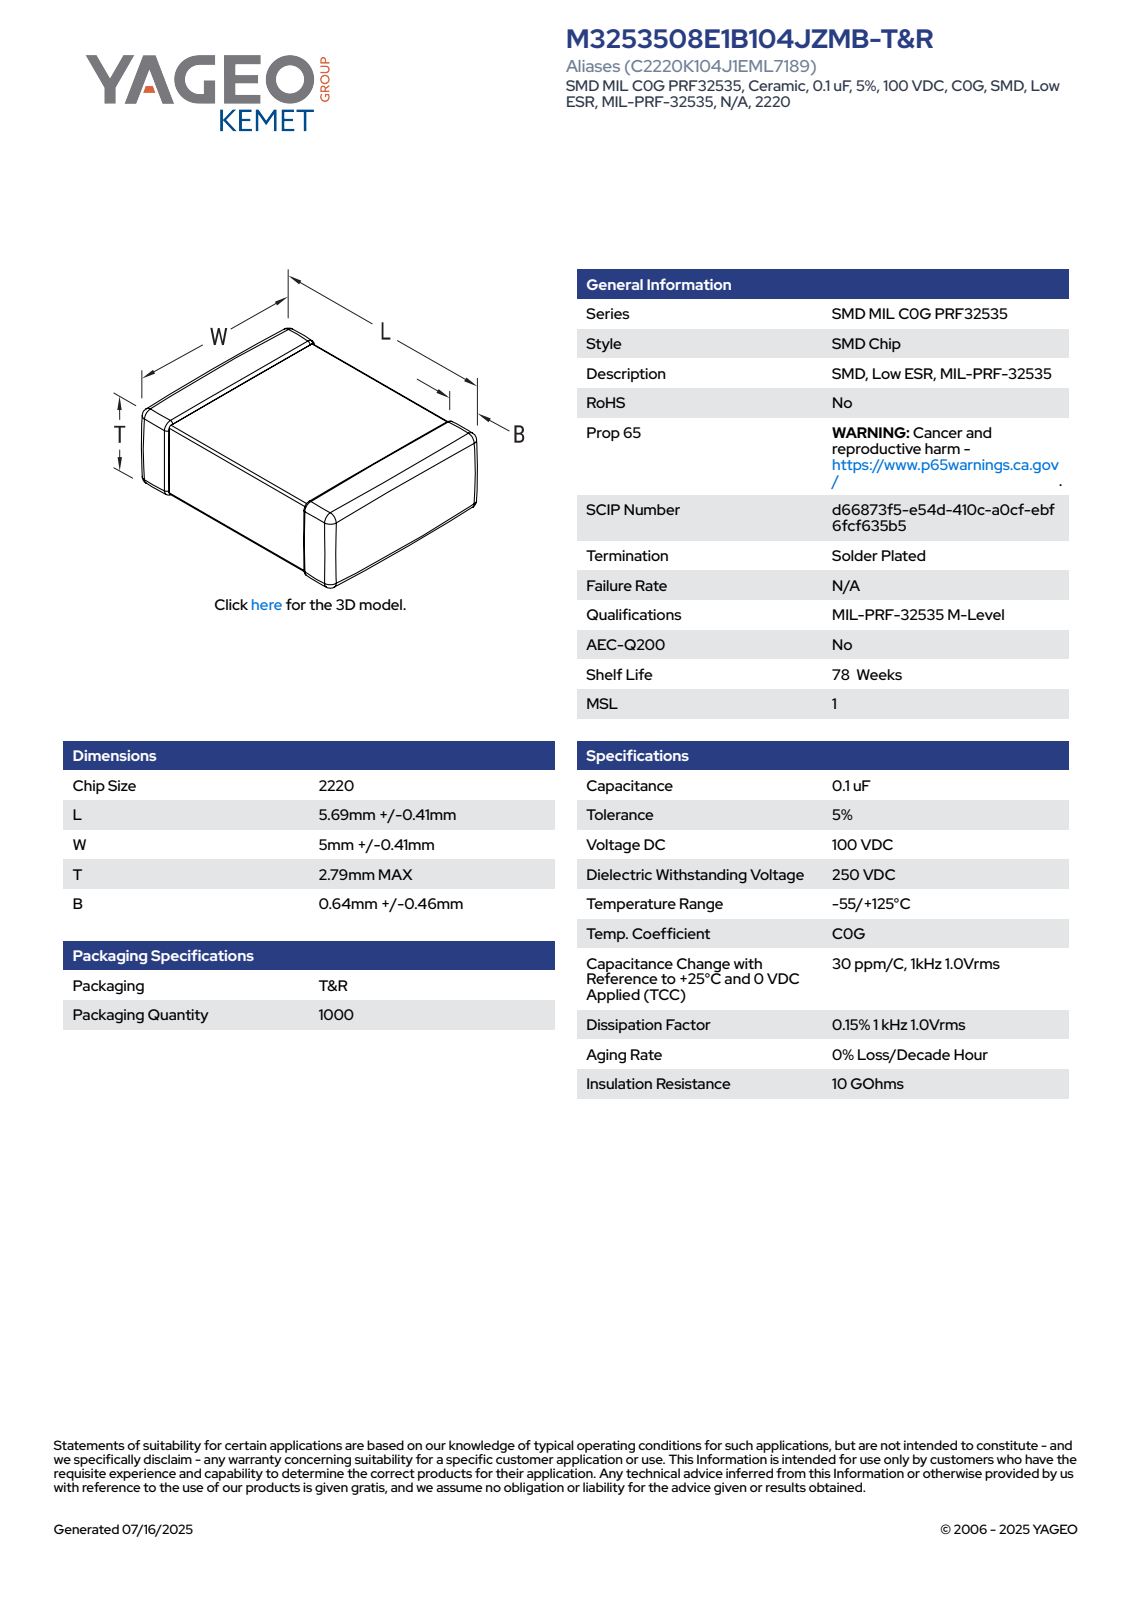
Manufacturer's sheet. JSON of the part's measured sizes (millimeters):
{"part_name": "CCS_STDNOS_2220_L6.1W5.41T2.79B0.64", "step_written_by": "SolidWorks 2014 (AUTOMOTIVE_DESIGN)", "units": "millimeters", "bodies": {"solids": 4, "faces": 129, "planar": 71, "cylindrical": 42, "other": 16}, "overall_size": [6.1, 5.41, 2.79], "volume_mm3": 83, "surface_area_mm2": 128, "partial_cylinders_radius": [[0.11, 24]], "face_to_face_distances": [2.57, 6.1, 5.19, 2.68, 2.79, 5.3, 5.41, 0.64, 2.46, 2.35]}
